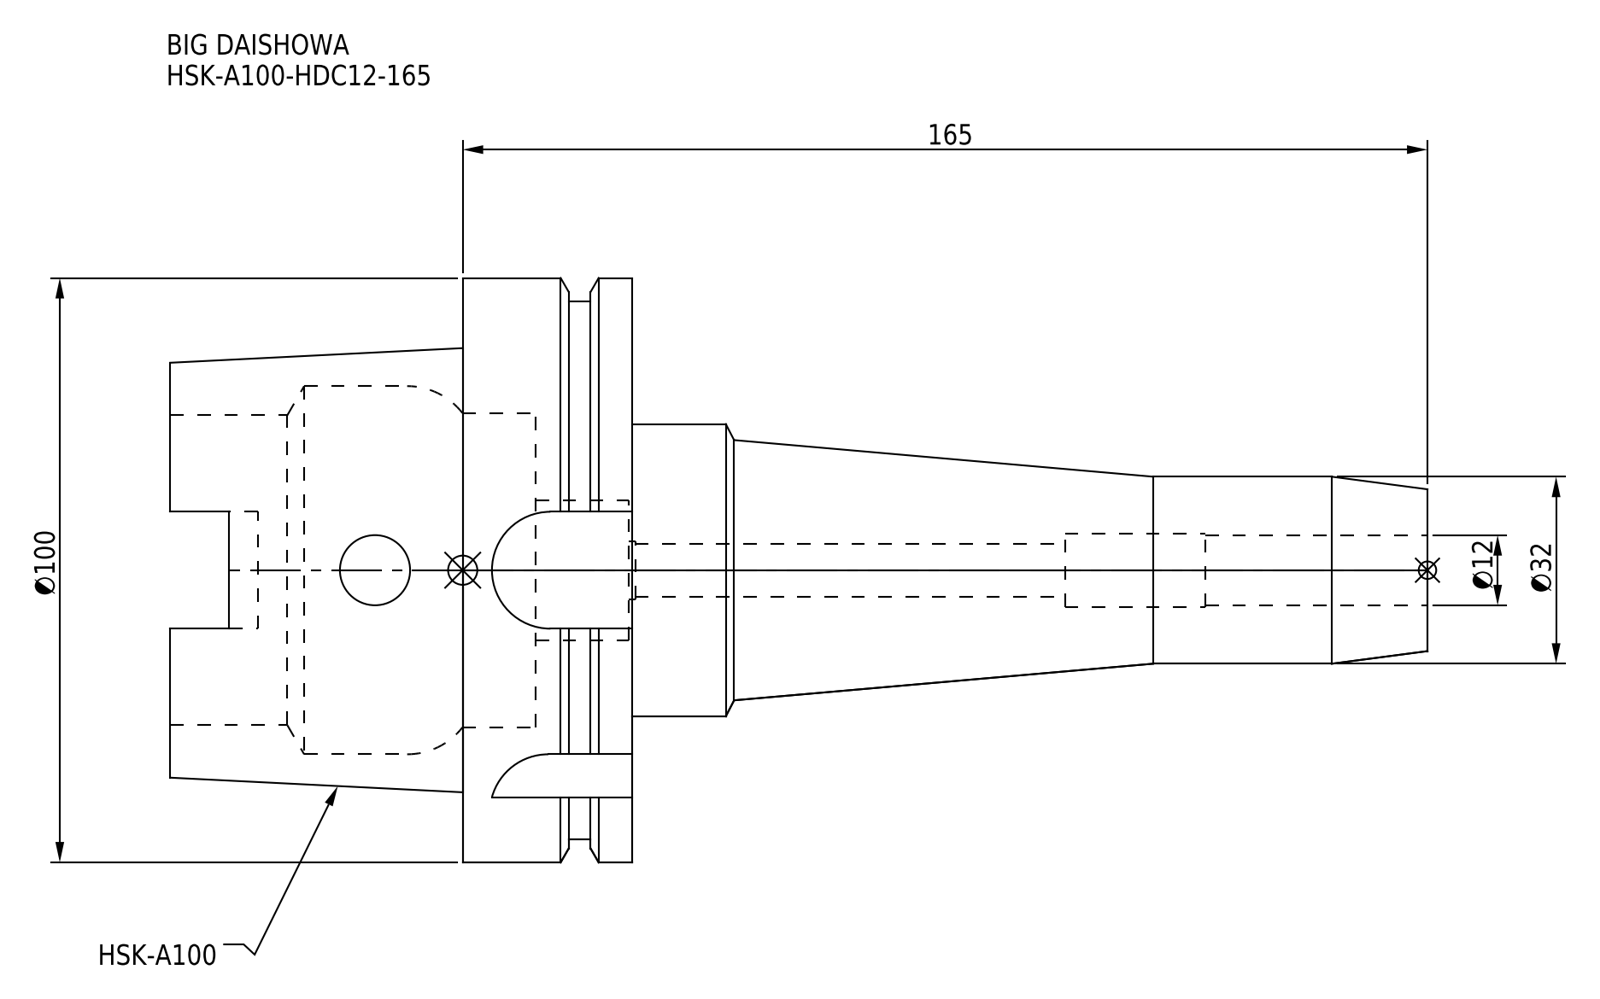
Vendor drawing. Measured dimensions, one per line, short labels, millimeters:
name: HSK-A100-HDC12-165
written by: CREO PARAMETRIC BY PTC INC, 2016380 (AUTOMOTIVE_DESIGN)
unit: mm
bodies: 1 solid, 97 faces (35 planar, 42 cylindrical, 20 other)
size: 215 × 100 × 100
volume: 394 581 mm³; area: 69 249 mm²
holes: 2× ⌀12, 1× ⌀9, 1× ⌀10, 1× ⌀12.5, 1× ⌀24, 1× ⌀53, 1× ⌀53.8, 1× ⌀63
bosses: 1× ⌀100, 1× ⌀92, 1× ⌀50, 1× ⌀32
rounds: 4× R4.88, 4× R10
face distances: 29, 16.55, 12.45, 79, 62.45, 50, 136, 152.55, 165, 215
